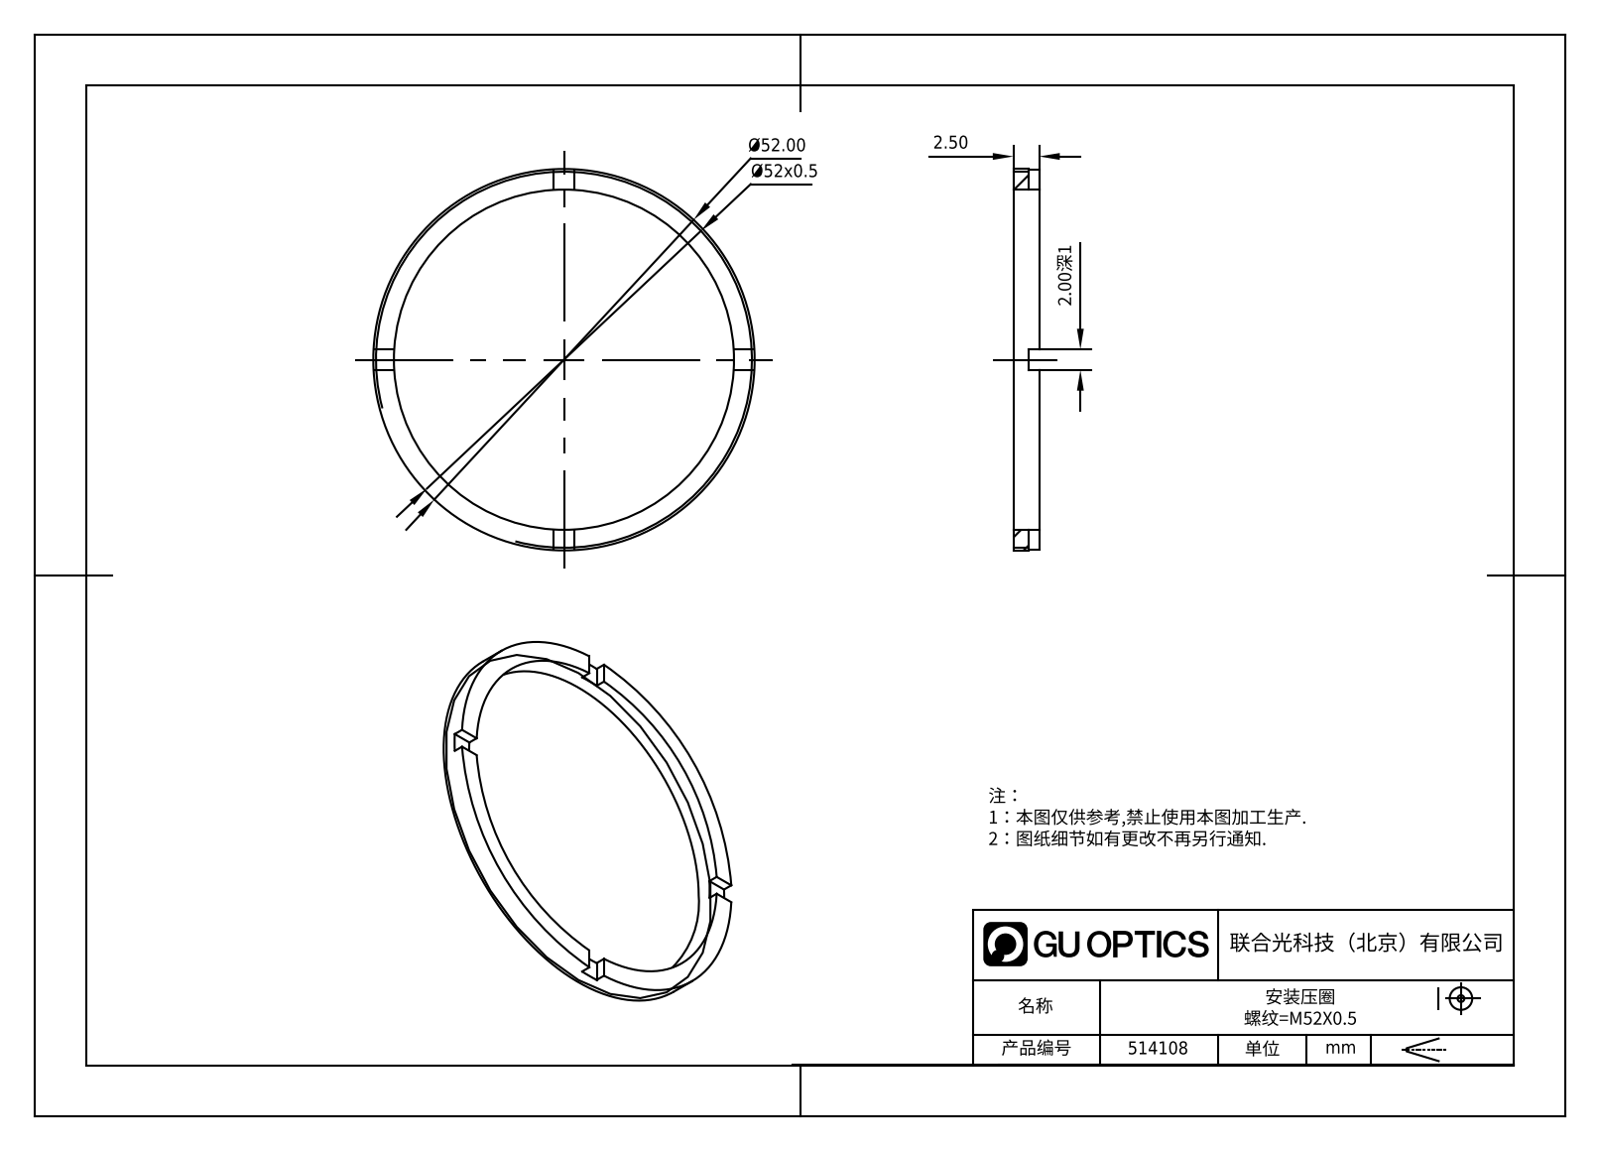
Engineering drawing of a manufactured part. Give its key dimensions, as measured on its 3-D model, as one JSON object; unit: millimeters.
{"part_name": "514108", "step_written_by": "SolidWorks 2020 (CONFIG_CONTROL_DESIGN)", "units": "millimeters", "bodies": {"solids": 1, "faces": 21, "planar": 17, "cylindrical": 4, "other": 0}, "overall_size": [52, 52, 2.5], "volume_mm3": 952, "surface_area_mm2": 1559, "round_holes": [[47, 1]], "round_bosses_or_shafts": [[52, 1]], "face_to_face_distances": [2.5, 1.5, 1, 2]}
